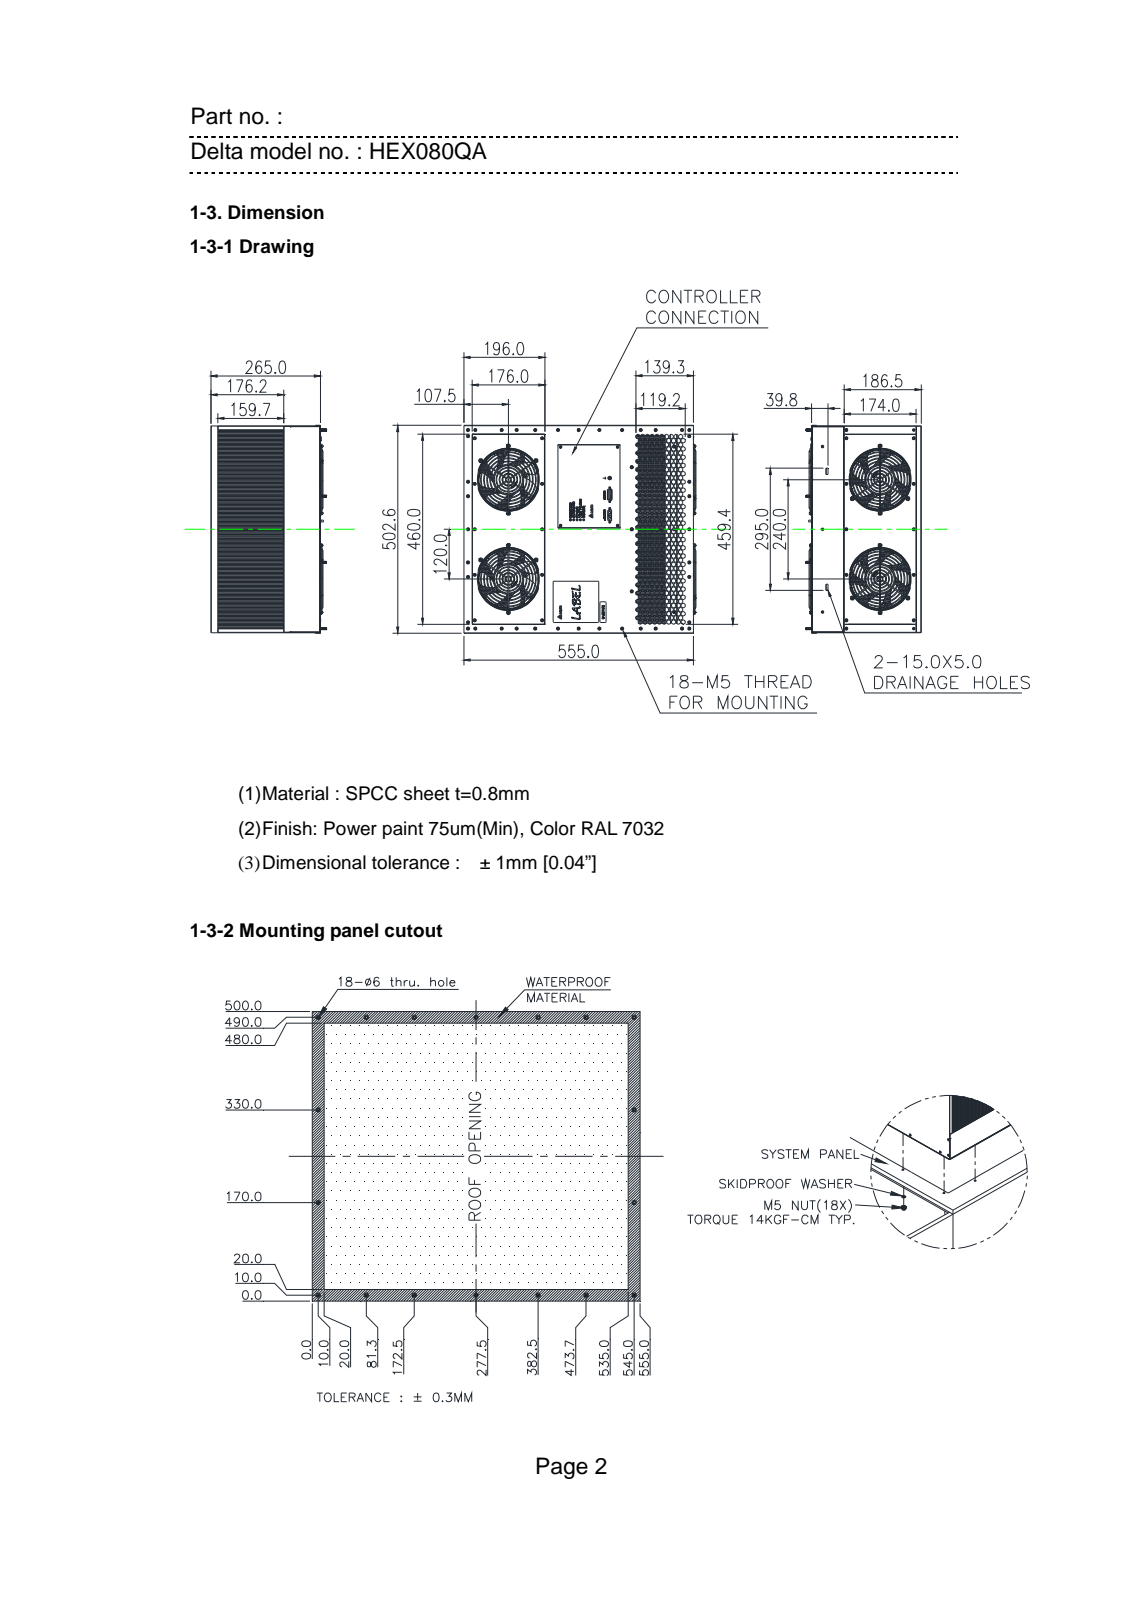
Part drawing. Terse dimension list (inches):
name: HEX080QA
written by: SolidWorks 2011 (CONFIG_CONTROL_DESIGN)
unit: in
bodies: 1 solid, 157 faces (97 planar, 60 cylindrical, 0 other)
size: 21.953 × 19.787 × 11.024
volume: 4 449 in³; area: 1 765 in²
bosses: 19× ⌀0.157, 5× ⌀0.197
rounds: 4× R3.012
face distances: 0.118, 19.685, 10.433, 21.732, 10.315, 0.02, 21.85, 0.098, 10.413, 21.614
